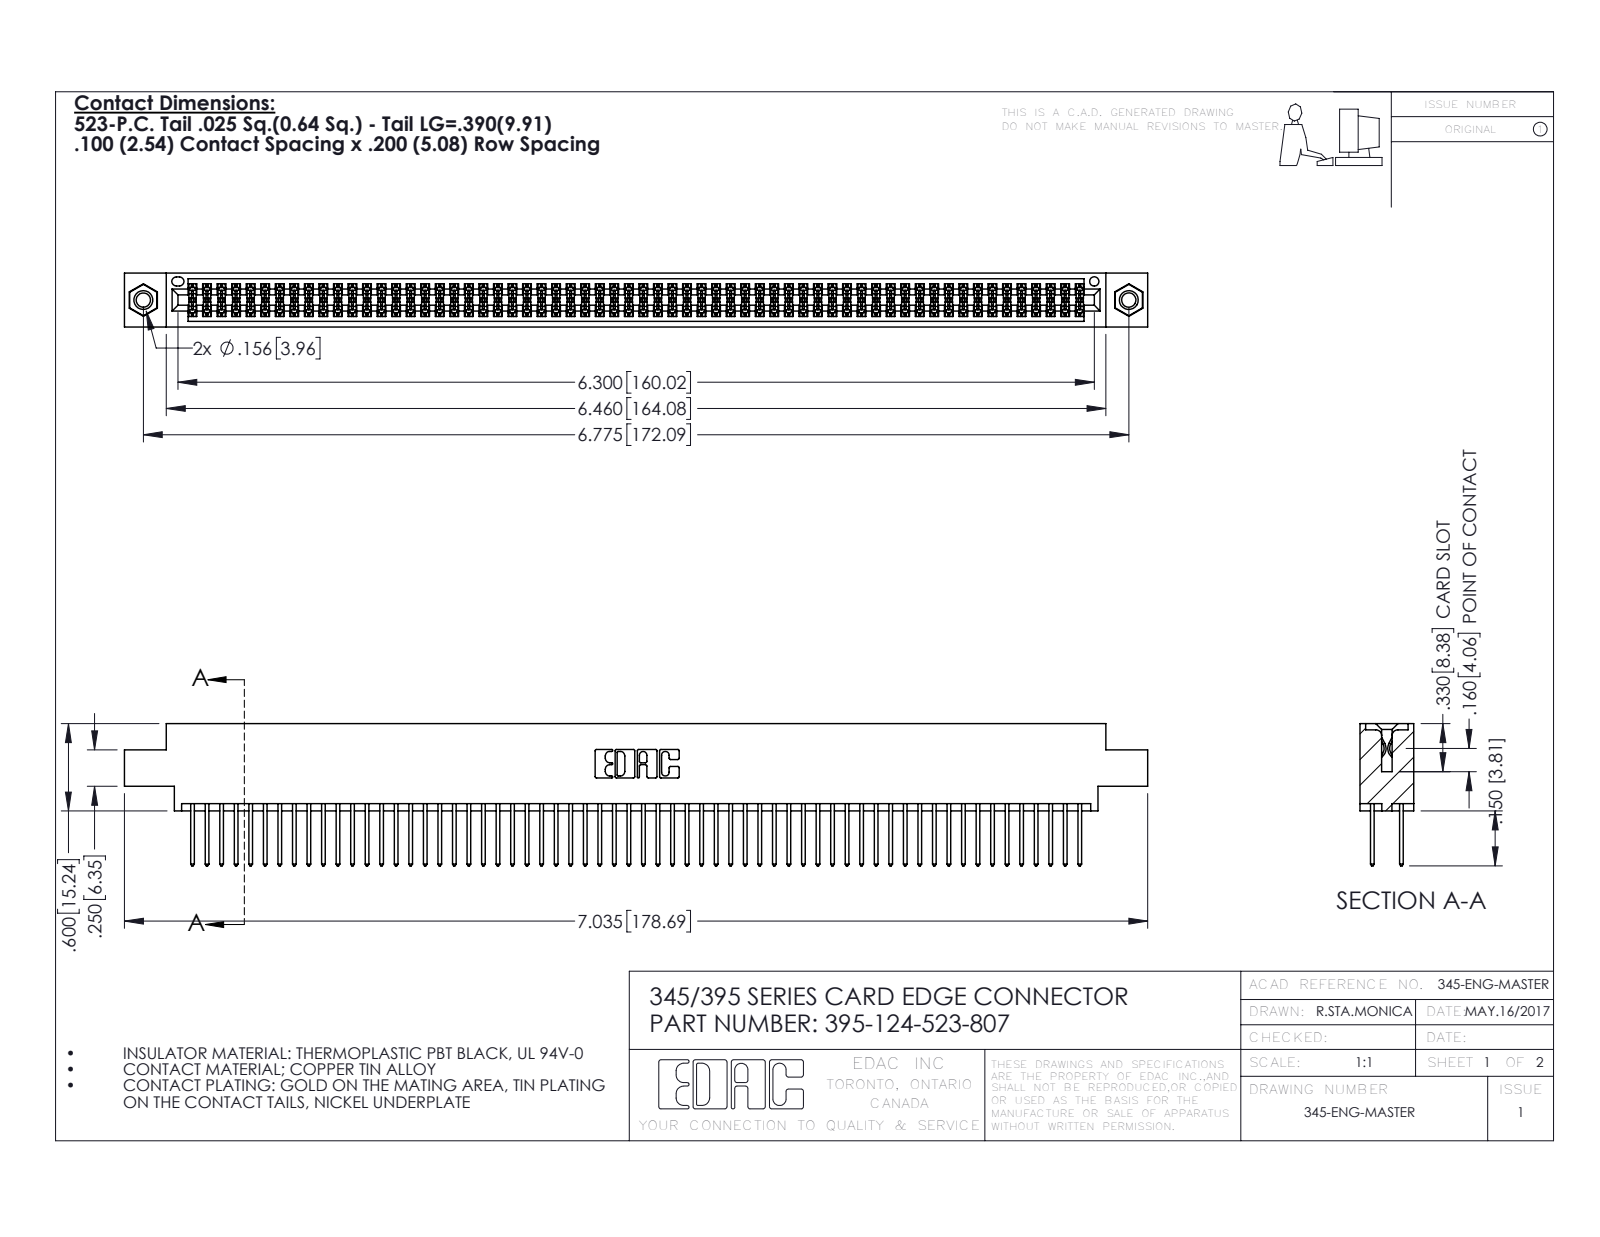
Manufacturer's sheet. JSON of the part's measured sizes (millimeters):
{"part_name": "345 Part_0.170 Offset - 0.156 Dia-TI; 345-250-001_345-250-005-103; 345-292-001_345-293-123; 395-124-523-807", "step_written_by": "SolidWorks 2016 (CONFIG_CONTROL_DESIGN)", "units": "millimeters", "bodies": {"solids": 127, "faces": 6390, "planar": 4208, "cylindrical": 2166, "other": 16}, "overall_size": [178.7, 24.8, 9.4], "volume_mm3": 17670, "surface_area_mm2": 27820, "round_holes": [[2.5, 2], [3.2, 2], [4, 2], [1.6, 1]], "round_bosses_or_shafts": [[3.9, 2]], "partial_cylinders_radius": [[0.2, 186], [0.3, 124], [0.3, 22], [0.2, 6], [0.8, 6], [0.7, 3], [0.4, 2], [0.5, 2]], "face_to_face_distances": [1.8, 7.6, 5.1, 2.5, 6.9, 0.6, 9.4, 5.7, 4.4, 3.8], "hole_center_spacings": [6.9, 166.1, 172.1]}
